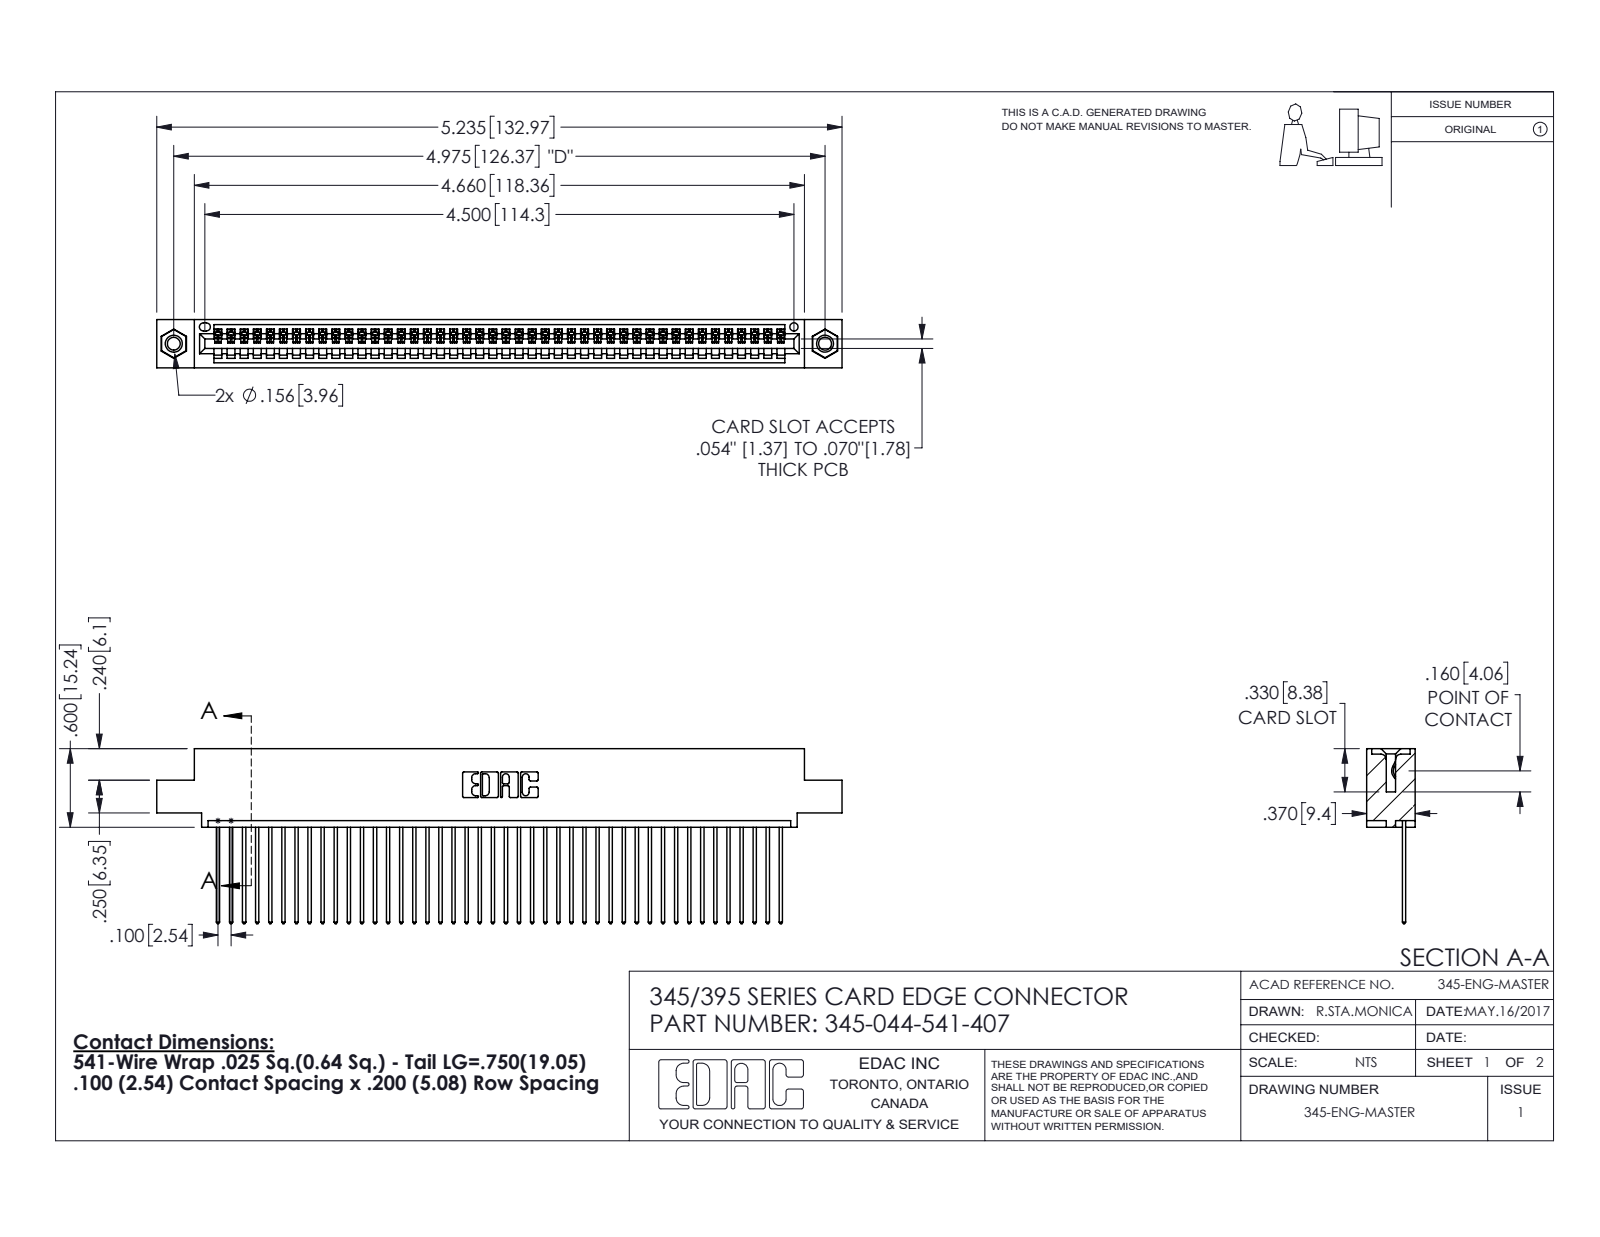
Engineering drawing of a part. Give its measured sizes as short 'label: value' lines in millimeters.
name: 345-250-001_345-250-005-103; 345-292-001_345-293-141; 345 Part_0.110 Offset - 0.156 Dia-TI; 345-044-541-407
written by: SolidWorks 2016 (CONFIG_CONTROL_DESIGN)
unit: mm
bodies: 47 solids, 2742 faces (1876 planar, 850 cylindrical, 16 other)
size: 133 × 34 × 9.4
volume: 12 700 mm³; area: 17 880 mm²
holes: 2× ⌀2.5, 2× ⌀3.2, 2× ⌀4, 1× ⌀1.6
bosses: 2× ⌀3.9
rounds: 88× R0.2, 88× R0.3, 22× R0.3, 6× R0.2, 6× R0.8, 3× R0.7, 2× R0.8, 2× R1
face distances: 1.8, 7.6, 2.5, 6.9, 0.6, 9.4, 5.1, 5.7, 3.8, 1.8
hole spacings: 6.9, 120.4, 126.4
